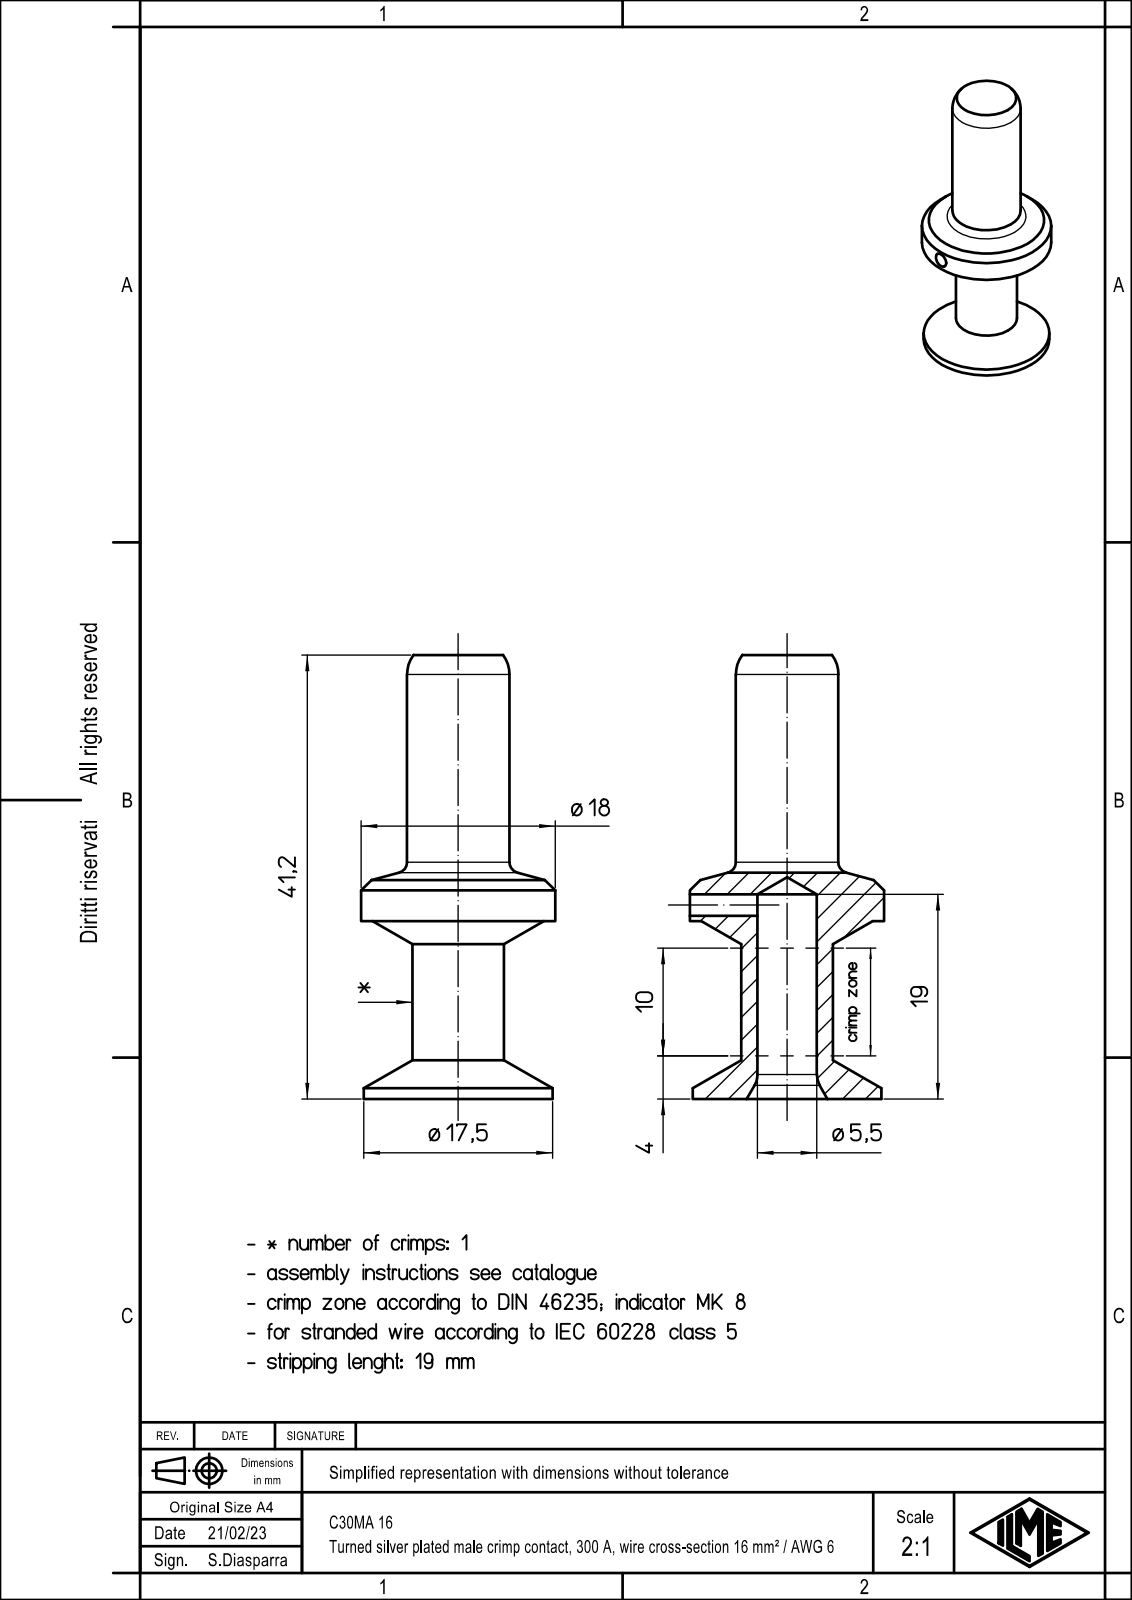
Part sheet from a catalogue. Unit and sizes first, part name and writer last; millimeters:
Units: millimetres
Overall size (bounding box): 41.2 × 18 × 18
Round holes (diameter × count): ⌀2 ×1, ⌀5.5 ×1
Round bosses / shafts (diameter × count): ⌀18 ×1, ⌀17.5 ×1, ⌀9.5 ×1, ⌀8.5 ×1
Main face-to-face distances: 16.5, 41.2, 24.7
Volume: 3 440 mm³ · Surface area: 2 388 mm²
Bodies: 1 solid, 33 faces (3 planar, 12 cylindrical, 18 other)
Part name (STEP PRODUCT): C30MA 16
STEP written by: Creo Elements/Direct Modeling 20.1B 02-Apr-2019 (C) Parametric Technology GmbH (AUTOMOTIVE_DESIGN)
